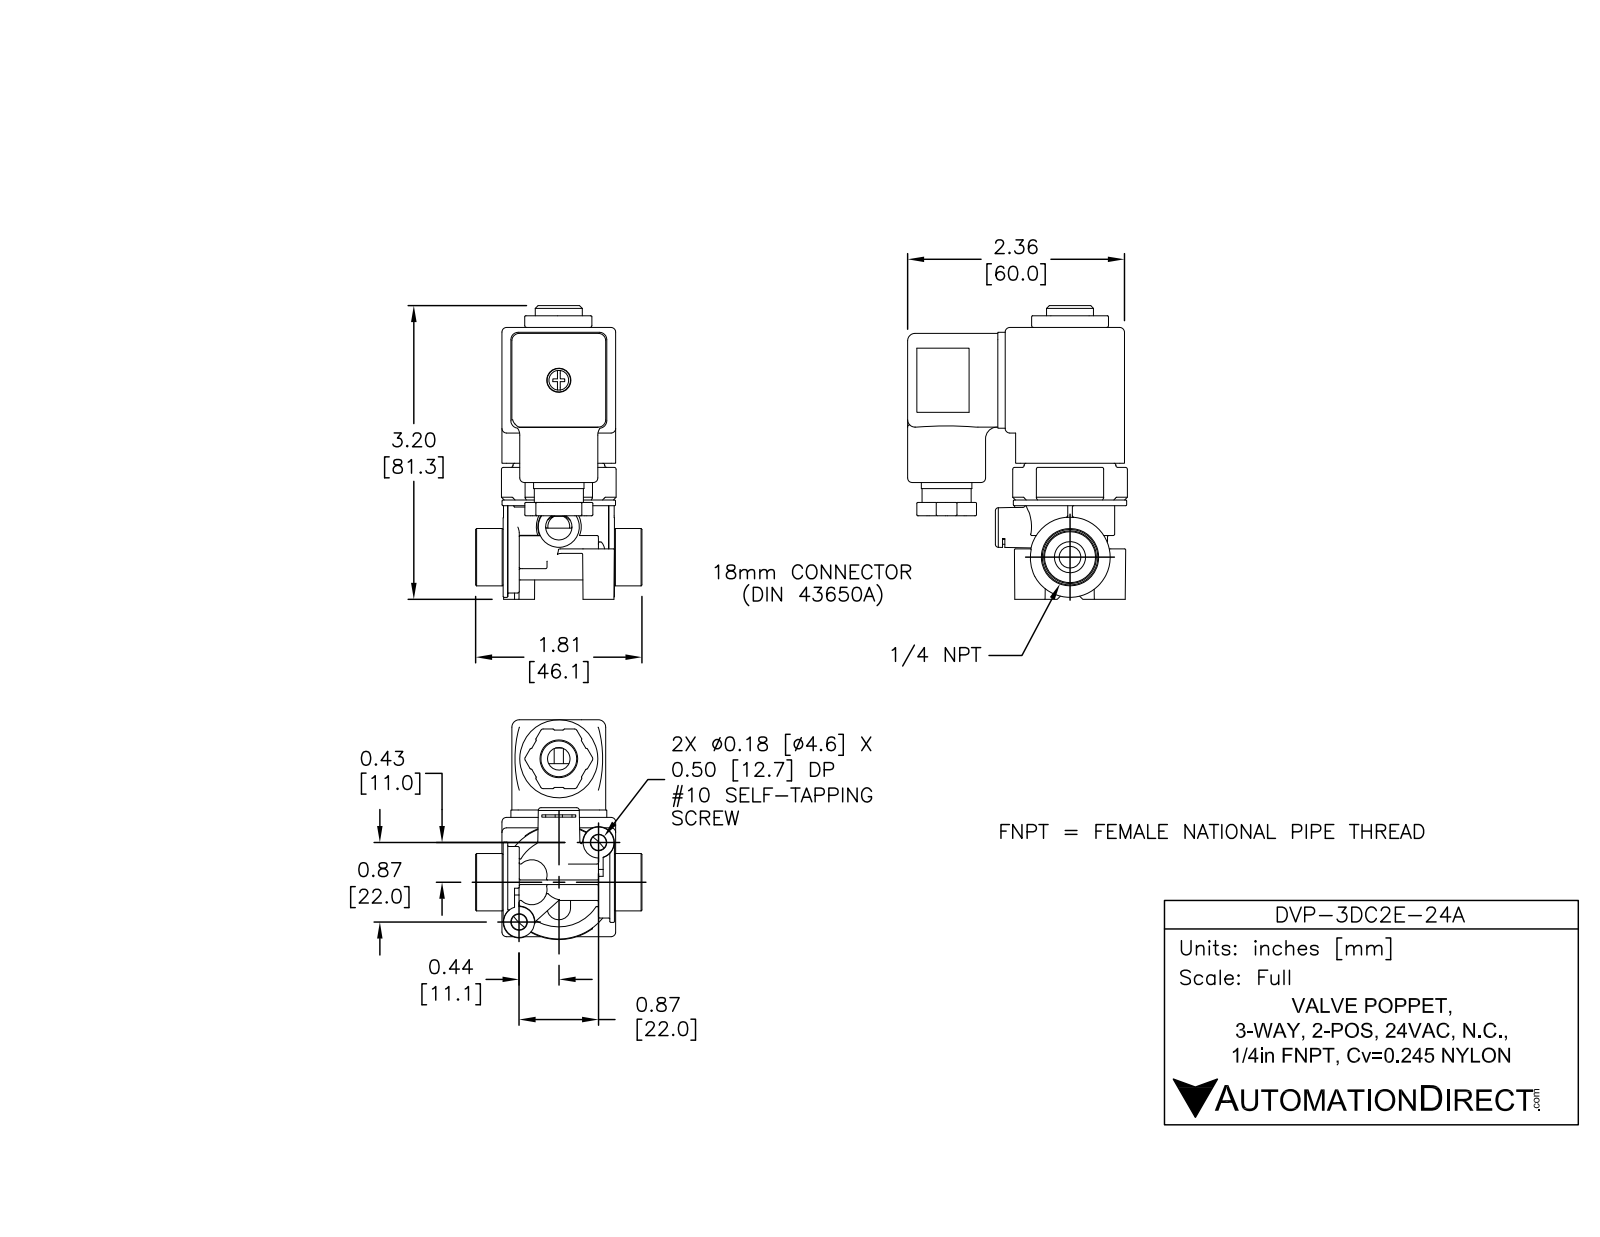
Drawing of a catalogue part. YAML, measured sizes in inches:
part_name: "DVP-3DC2E-24A"
step_written_by: "SolidWorks 2015 (AUTOMOTIVE_DESIGN)"
units: inches
bodies: {solids: 7, faces: 1850, planar: 809, cylindrical: 362, other: 679}
overall_size: [3.204, 2.395, 1.813]
volume: 3.912
surface_area: 55.24
round_holes:
  - {diameter: 0.06, count: 2}
  - {diameter: 0.236, count: 2}
  - {diameter: 0.093, count: 1}
  - {diameter: 0.095, count: 1}
  - {diameter: 0.102, count: 1}
  - {diameter: 0.12, count: 1}
  - {diameter: 0.137, count: 1}
  - {diameter: 0.203, count: 1}
  - {diameter: 0.245, count: 1}
  - {diameter: 0.25, count: 1}
  - {diameter: 0.263, count: 1}
  - {diameter: 0.287, count: 1}
round_bosses_or_shafts:
  - {diameter: 0.29, count: 2}
  - {diameter: 1.236, count: 1}
  - {diameter: 1, count: 1}
  - {diameter: 0.972, count: 1}
  - {diameter: 0.922, count: 1}
  - {diameter: 0.89, count: 1}
  - {diameter: 0.875, count: 1}
  - {diameter: 0.85, count: 1}
partial_cylinders:
  - {radius: 0.01, count: 75}
  - {radius: 0.015, count: 38}
  - {radius: 0.05, count: 21}
  - {radius: 0.02, count: 12}
  - {radius: 0.08, count: 12}
  - {radius: 0.026, count: 6}
  - {radius: 0.03, count: 6}
  - {radius: 0.04, count: 4}
face_to_face_distances: [1.083, 1.24, 0.048, 0.157, 0.925, 1.416, 1.48, 0.109, 1.131, 0.974]
hole_center_spacings: [0.281, 0.283, 1.062, 1.343, 1.345, 1.612, 1.626, 2.184]
